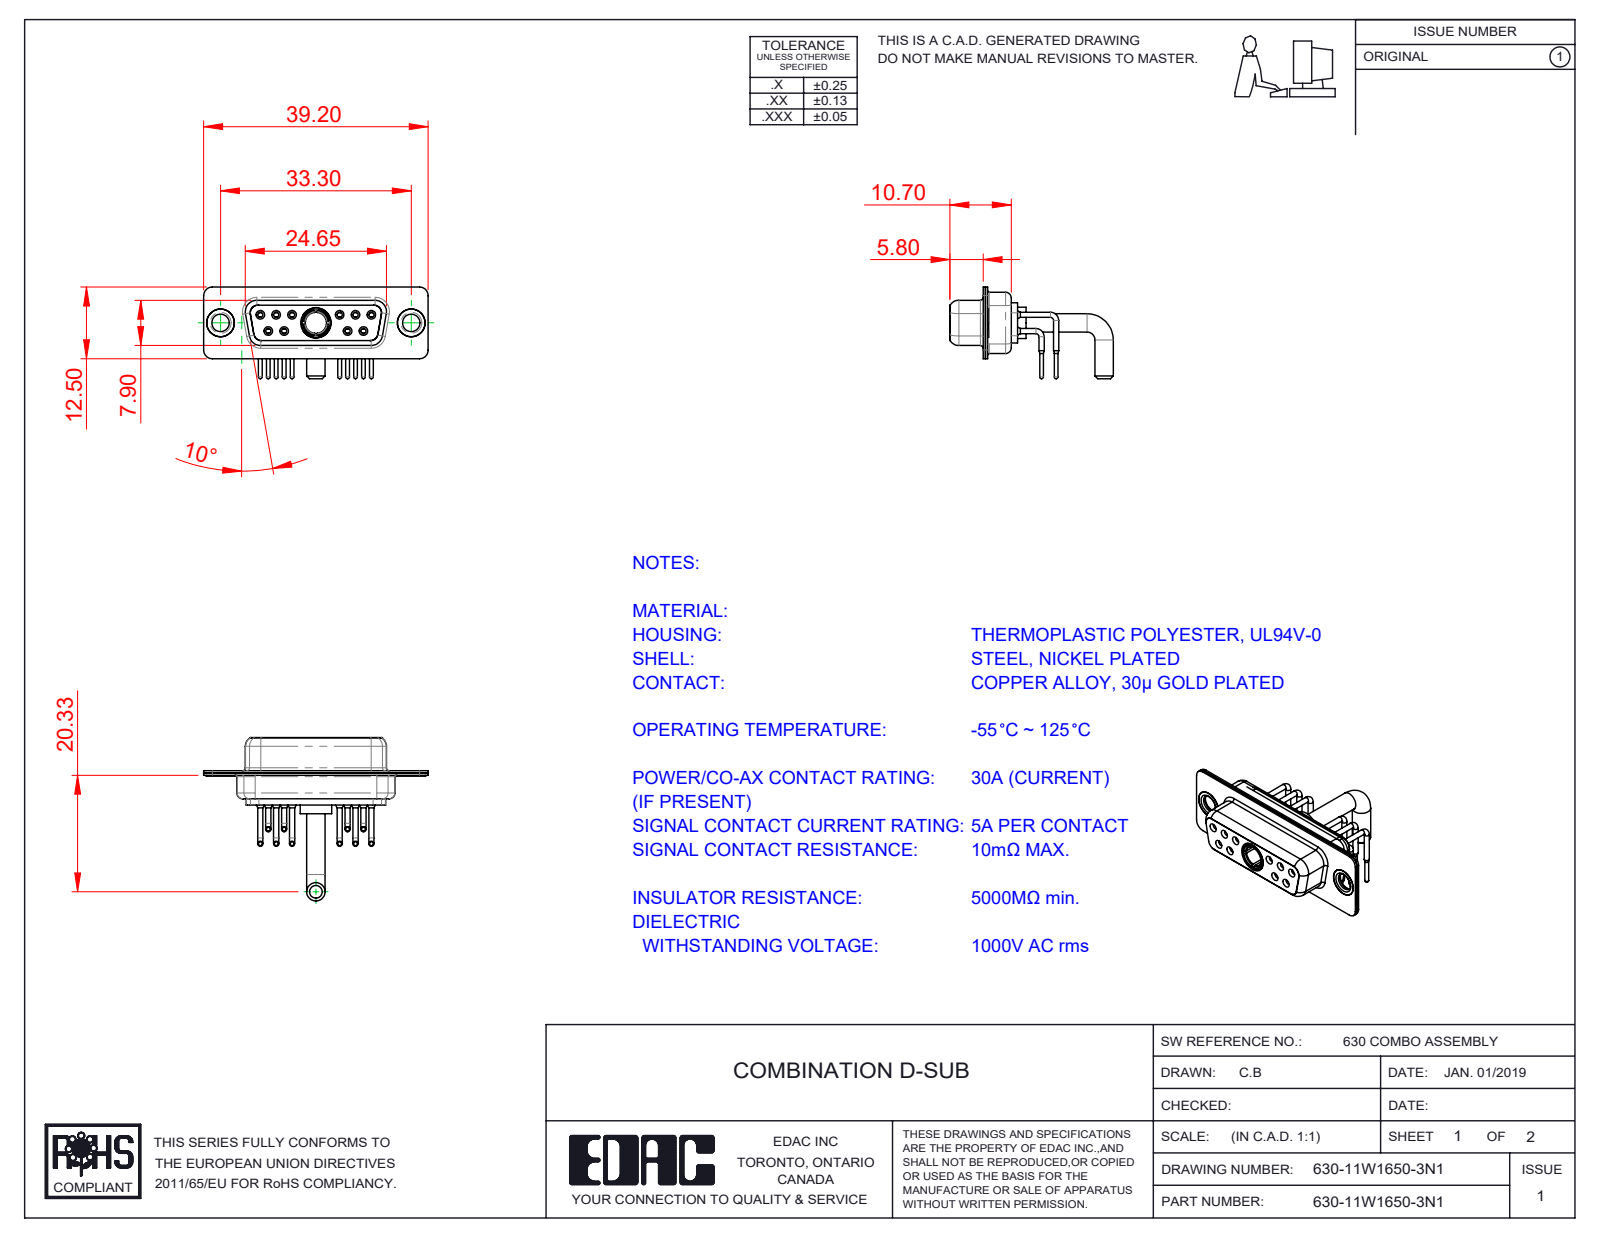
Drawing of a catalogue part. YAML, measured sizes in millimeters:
part_name: "630Combo Contact Row 2; Power Socket_Ext 30A RA; 630Combo Contact Row 1; 630Combo Shell Front_15 Contacts (+4 more)"
step_written_by: "SolidWorks 2020 (CONFIG_CONTROL_DESIGN)"
units: millimeters
bodies: {solids: 17, faces: 861, planar: 246, cylindrical: 376, other: 239}
overall_size: [39.2, 28.53, 16]
volume: 2654
surface_area: 6217
round_holes:
  - {diameter: 0.9, count: 10}
  - {diameter: 1.1, count: 10}
  - {diameter: 1.5, count: 10}
  - {diameter: 2, count: 10}
  - {diameter: 1.7, count: 6}
  - {diameter: 1.6, count: 4}
  - {diameter: 4.85, count: 3}
  - {diameter: 3.05, count: 2}
  - {diameter: 4, count: 2}
  - {diameter: 4.05, count: 2}
  - {diameter: 3.7, count: 1}
  - {diameter: 5.3, count: 1}
round_bosses_or_shafts:
  - {diameter: 0.9, count: 10}
  - {diameter: 0.65, count: 10}
  - {diameter: 1.6, count: 6}
  - {diameter: 5, count: 2}
  - {diameter: 4.95, count: 2}
  - {diameter: 4.8, count: 2}
  - {diameter: 3.55, count: 2}
  - {diameter: 3.2, count: 2}
partial_cylinders:
  - {radius: 1.5, count: 16}
  - {radius: 1.35, count: 12}
  - {radius: 2, count: 12}
  - {radius: 1.6, count: 8}
  - {radius: 0.25, count: 4}
  - {radius: 0.5, count: 4}
  - {radius: 0.6, count: 4}
  - {radius: 0.65, count: 4}
face_to_face_distances: [0.4, 1.4, 0.45, 8.45, 1.8, 8.9, 6.2, 0.8, 7.05, 1.85]
hole_center_spacings: [3.16, 2.77, 13.85, 11.08, 16.62, 5.03, 5.04, 5.54]
